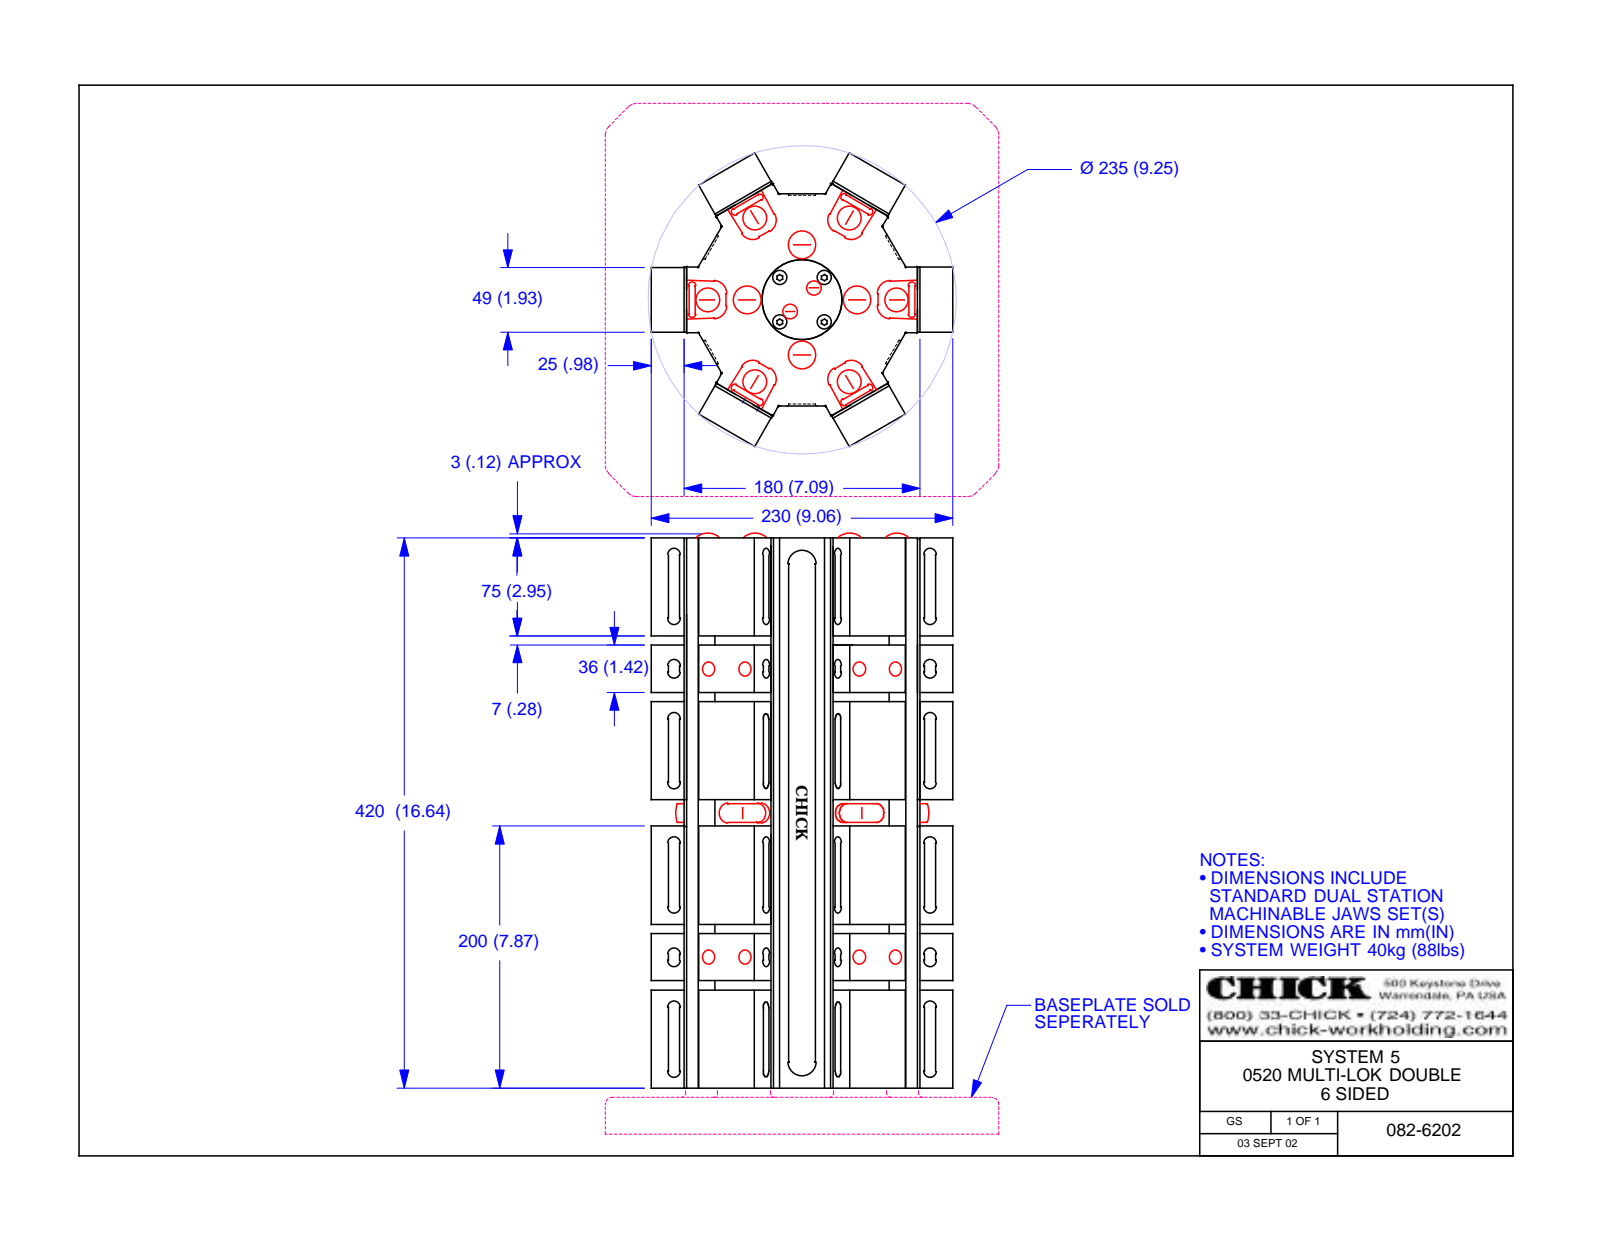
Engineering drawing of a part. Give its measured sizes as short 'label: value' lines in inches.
name: 082-6202; 082-6212; 080-0313-21; 080-2500 (+2 more)
written by: Autodesk Inventor 2013 (AUTOMOTIVE_DESIGN)
unit: in
bodies: 49 solids, 5361 faces (1978 planar, 1239 cylindrical, 2144 other)
size: 16.693 × 9.055 × 8.791
volume: 668.2 in³; area: 1 978 in²
holes: 60× ⌀0.5, 36× ⌀0.163, 36× ⌀0.394, 20× ⌀0.205, 20× ⌀0.38, 12× ⌀0.36, 7× ⌀0.787, 6× ⌀0.398, 5× ⌀0.531, 4× ⌀0.728, 3× ⌀0.541, 2× ⌀0.262
bosses: 36× ⌀0.551, 3× ⌀0.604, 3× ⌀0.375
rounds: 340× R0.031, 36× R0.039, 24× R0.075, 24× R0.197, 20× R0.094, 12× R0.311, 12× R0.344, 12× R0.437
face distances: 0.079, 7.008, 1.063, 0.984, 7.992, 8.071, 2.913, 3.465, 6.929, 7.087
hole spacings: 2.953, 3.21, 8.661, 1.26, 5.906, 8.753, 5.709, 5.846
